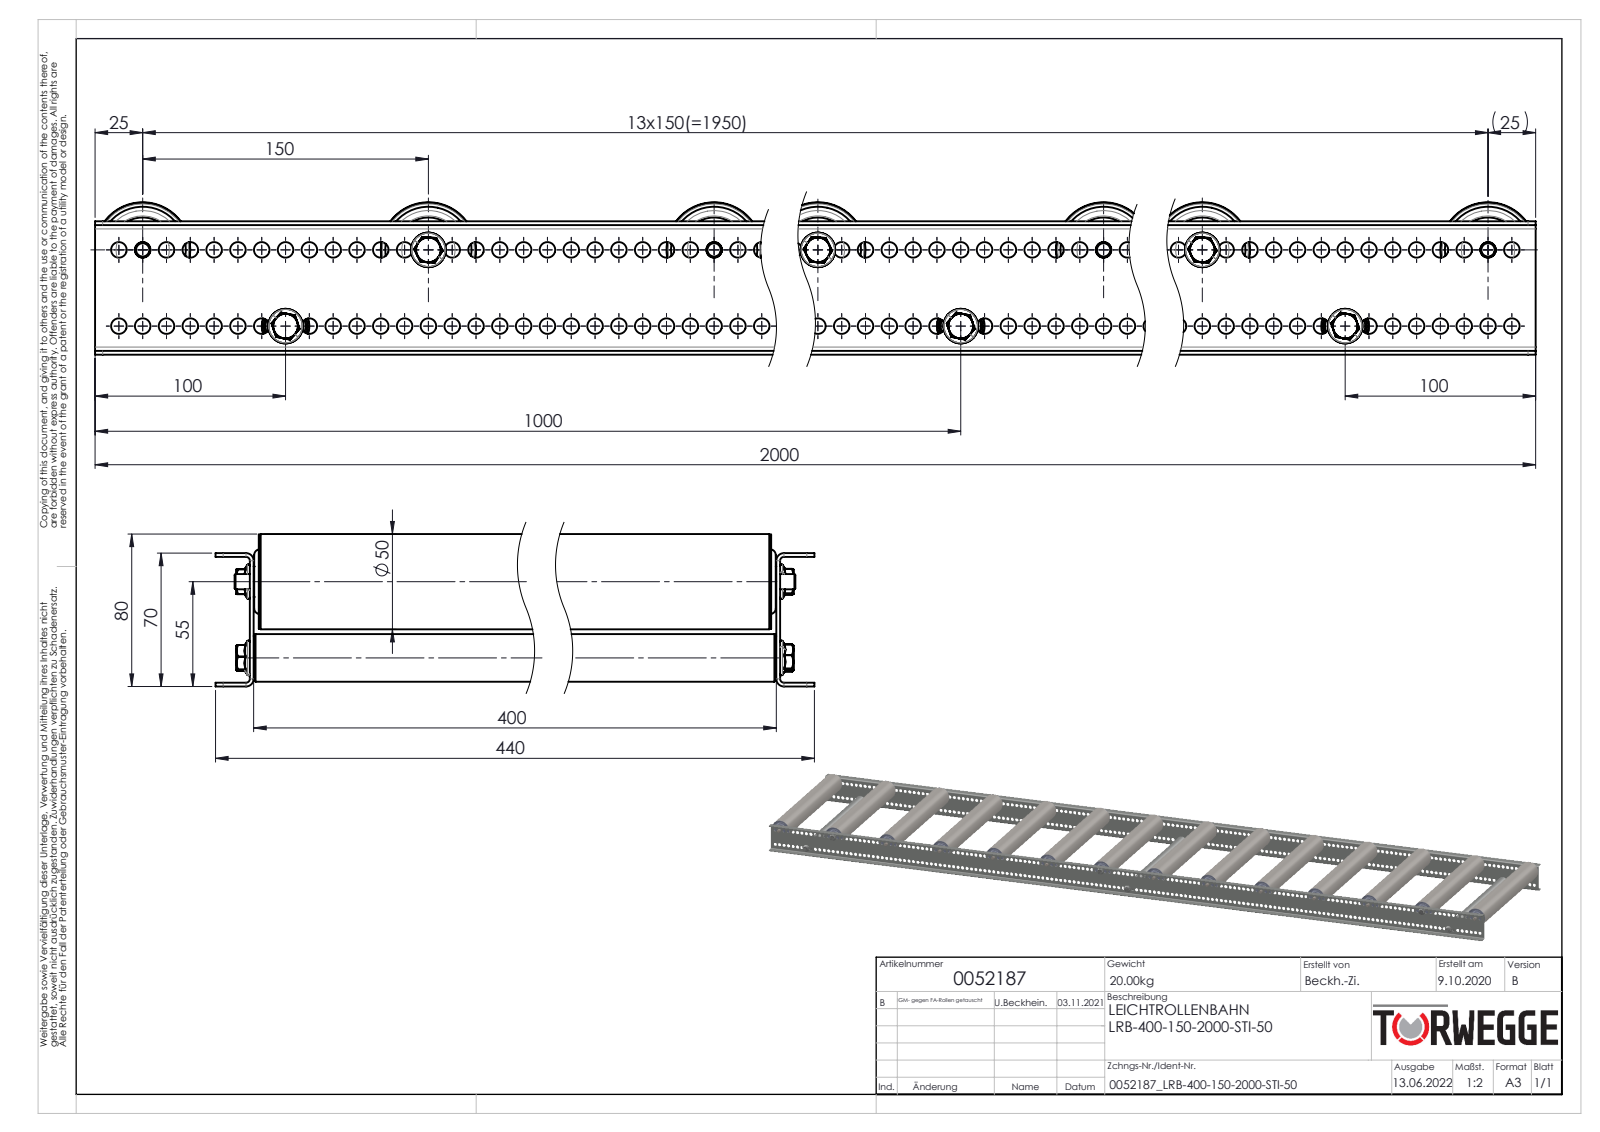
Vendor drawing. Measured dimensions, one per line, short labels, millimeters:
name: 0039771_Tragrollenrohr-Ø50x1,5STI_KFG_EL400; Tragrollenachse-Ø8_KFG_L=420; TRG-50x1,5-STI-A12-IGM8-EL=KFG_0022778TWG_TRG-50x1,5-STI-A12-IGM8-EL=400; Traversen_KFG_L400 (+8 more)
written by: SolidWorks 2020 (AUTOMOTIVE_DESIGN)
unit: mm
bodies: 350 solids, 6934 faces (1320 planar, 2752 cylindrical, 2862 other)
size: 2000 × 440 × 80
volume: 2 854 000 mm³; area: 3 256 000 mm²
holes: 318× ⌀8.2, 14× ⌀17.1, 14× ⌀18.5, 14× ⌀27.7, 14× ⌀45.3, 14× ⌀47, 11× ⌀7.6, 6× ⌀6.8, 3× ⌀12, 3× ⌀12.2, 3× ⌀19.2, 3× ⌀21
bosses: 17× ⌀8, 14× ⌀50, 14× ⌀49.5, 14× ⌀47.3, 14× ⌀29.7, 14× ⌀27.4, 14× ⌀27.3, 14× ⌀16
rounds: 22× R0.6, 22× R0.75, 22× R2.45, 12× R2.5, 11× R4.87, 11× R7, 8× R4, 4× R2
face distances: 2, 402, 68, 400, 404, 70, 66, 18, 20, 420
hole spacings: 12.5, 25, 37.5, 50, 62.5, 75, 87.5, 100
